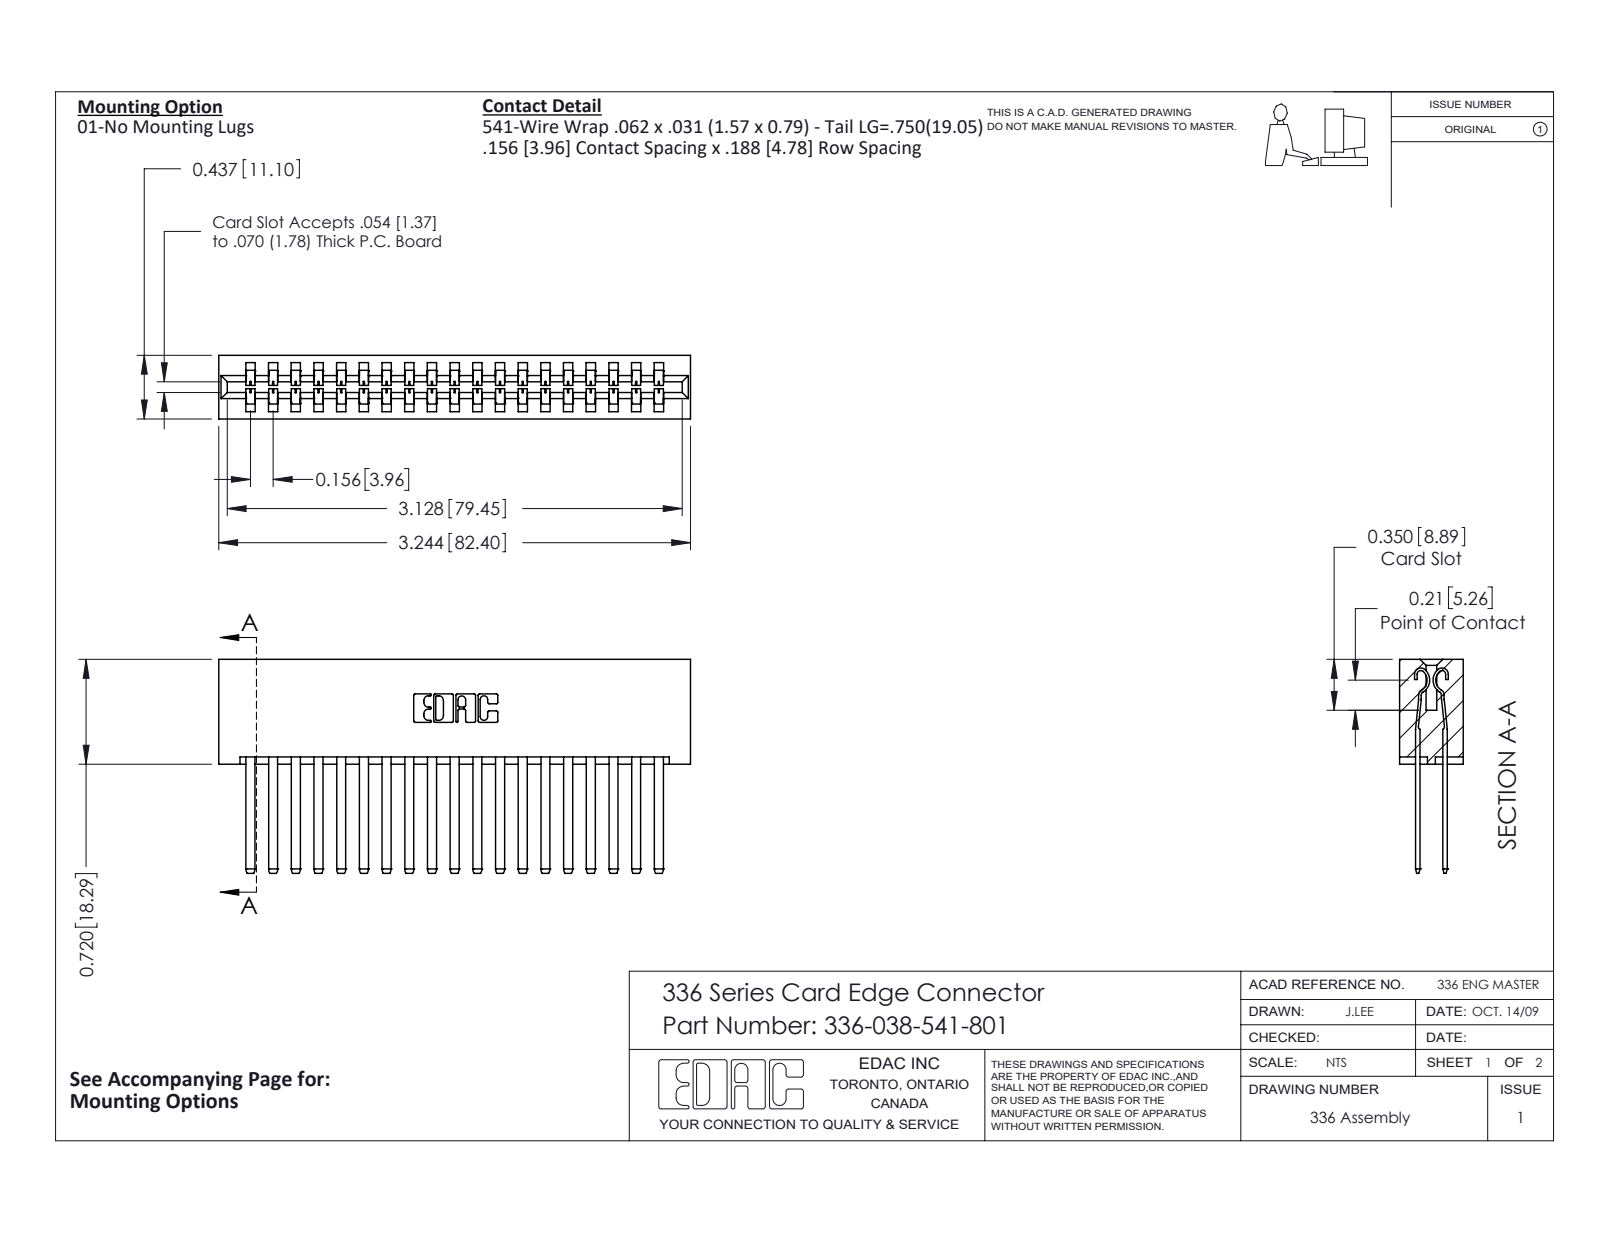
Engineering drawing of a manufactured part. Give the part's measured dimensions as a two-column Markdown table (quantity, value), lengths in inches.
| quantity | value |
| --- | --- |
| part name | 336-038-541-801; 336 Part_Lugless; 336-290-001_336-290-541 |
| STEP written by | SolidWorks 2020 (CONFIG_CONTROL_DESIGN) |
| units | inches |
| bodies | 39 solids, 1702 faces (1054 planar, 648 cylindrical, 0 other) |
| overall size | 3.244 × 1.47 × 0.437 |
| volume | 0.833 in³ |
| surface area | 26.6 in² |
| partial cylindrical surfaces (radius × count) | 0.004 × 76, 0.056 × 38, 0.01 × 22, 0.007 × 6, 0.031 × 6, 0.022 × 4, 0.04 × 4, 0.026 × 3 |
| main face-to-face distances | 0.188, 0.328, 0.14, 0.297, 0.109, 0.031, 0.437, 0.033, 0.181, 0.256 |
